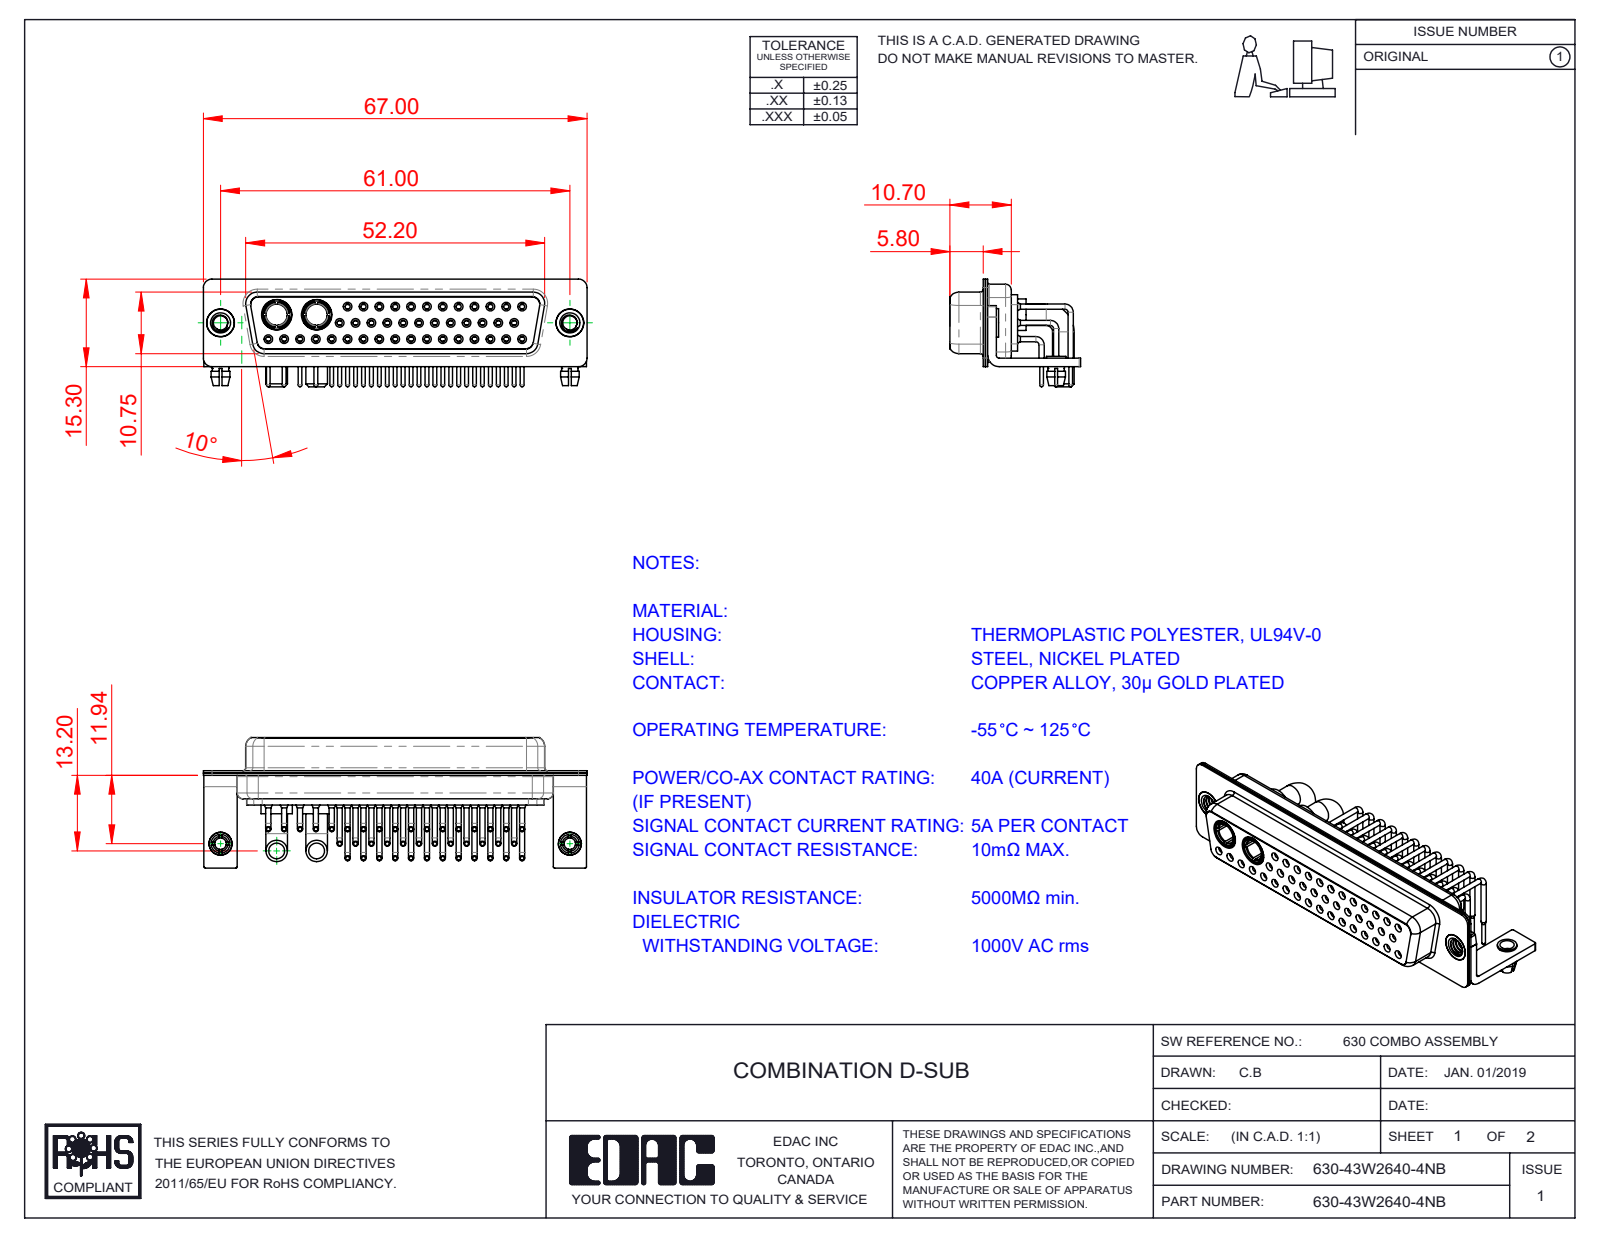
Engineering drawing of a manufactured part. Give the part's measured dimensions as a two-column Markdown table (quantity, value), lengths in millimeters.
| quantity | value |
| --- | --- |
| part name | 630Combo Housing_43W2; 630Combo Shell Front_50 Contacts; 630Combo Contact Row 3; 630Combo Shell Rear_50 Contacts (+7 more) |
| STEP written by | SolidWorks 2020 (CONFIG_CONTROL_DESIGN) |
| units | millimeters |
| bodies | 54 solids, 2738 faces (808 planar, 1180 cylindrical, 750 other) |
| overall size | 67 × 22.8 × 18.8 |
| volume | 7 771 mm³ |
| surface area | 16 881 mm² |
| round holes (diameter × count) | 2 × 43, 0.9 × 41, 1.1 × 41, 1.5 × 41, 1.6 × 29, 1.7 × 12, 2.5 × 4, 4.85 × 4, 3.2 × 2, 3.7 × 2, 4 × 2, 4.05 × 2 |
| round bosses / shafts (diameter × count) | 0.9 × 41, 0.65 × 41, 1.6 × 12, 3.75 × 4, 5.5 × 2, 5.2 × 2, 5 × 2, 4.96 × 2 |
| partial cylindrical surfaces (radius × count) | 0.25 × 16, 1.5 × 16, 2 × 13, 1.35 × 12, 1.6 × 8, 0.5 × 5, 0.6 × 4, 0.65 × 4 |
| main face-to-face distances | 0.4, 1.5, 6, 5.6, 0.8, 5.8, 5.2, 11.28, 1.82, 10.35 |
| hole center spacings | 2.77, 3.16, 5.54, 8.31, 11.08, 13.85, 16.62, 19.39 |
